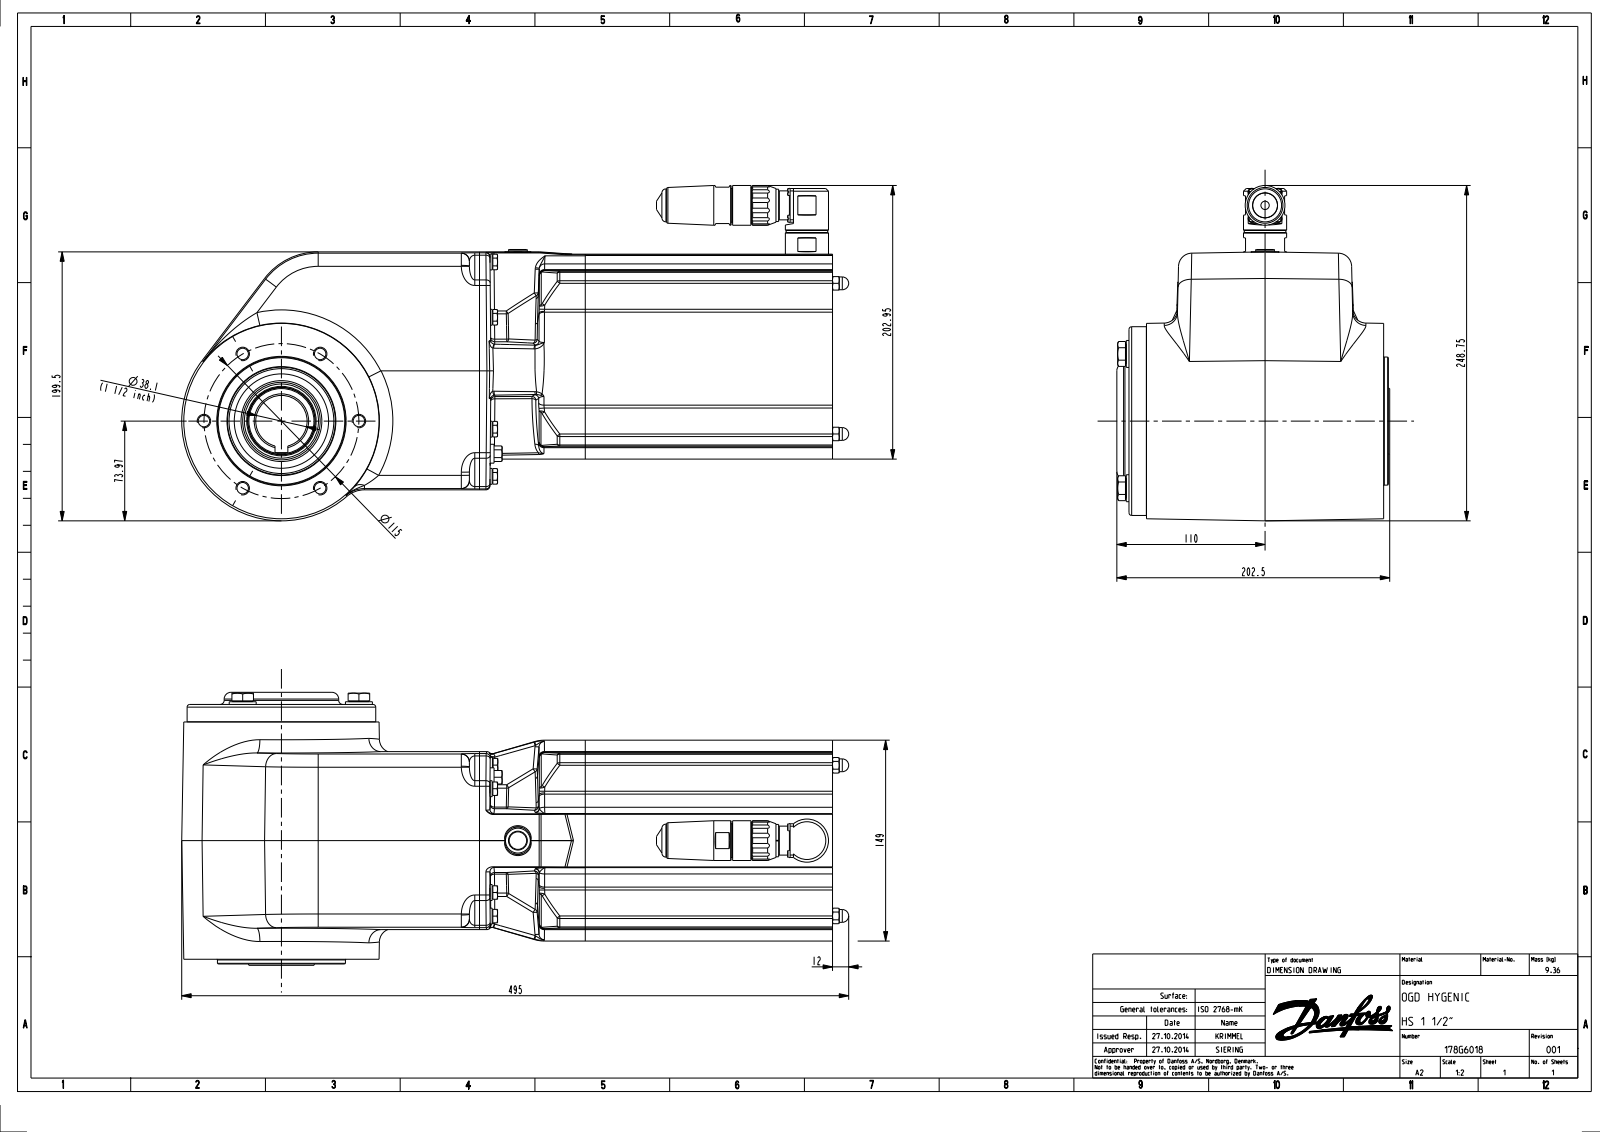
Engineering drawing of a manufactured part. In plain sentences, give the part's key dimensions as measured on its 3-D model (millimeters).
The part is named "178G6018_HUELLE_SW0001". Its 3-D file was written by "PRO/ENGINEER BY PARAMETRIC TECHNOLOGY CORPORATION, 2013230 (AUTOMOTIVE_DESIGN)". It is 1 solid with 1123 faces: 325 planar, 252 cylindrical and 546 other. Overall it measures 495 by 248.75 by 202.5 millimeters. Its volume is 10 290 000 cubic millimeters and its surface area 397 659 square millimeters. Round holes: 8 of diameter 6.1, 6 of diameter 8.5, 1 of diameter 38.1, 1 of diameter 38.5, 1 of diameter 40.49, 1 of diameter 49, 1 of diameter 70, 1 of diameter 80. Round bosses or shafts: 8 of diameter 11.8, 8 of diameter 9, 8 of diameter 6, 4 of diameter 9.5, 3 of diameter 20, 3 of diameter 14.63, 3 of diameter 14, 1 of diameter 140. Partial cylindrical surfaces (rounded edges, fillets, slot ends): 34 of radius 3, 16 of radius 4, 12 of radius 6, 8 of radius 0.5, 8 of radius 5, 6 of radius 10, 4 of radius 7, 4 of radius 20. The main face-to-face distances are 133.38, 176.5, 189, 3.5, 9, 198, 133.39, 192.5, 201.5, 7. The hole center spacings are 57.5, 99.59, 44.58, 77, 103.01, 119.29, 151.18, 57.48.
